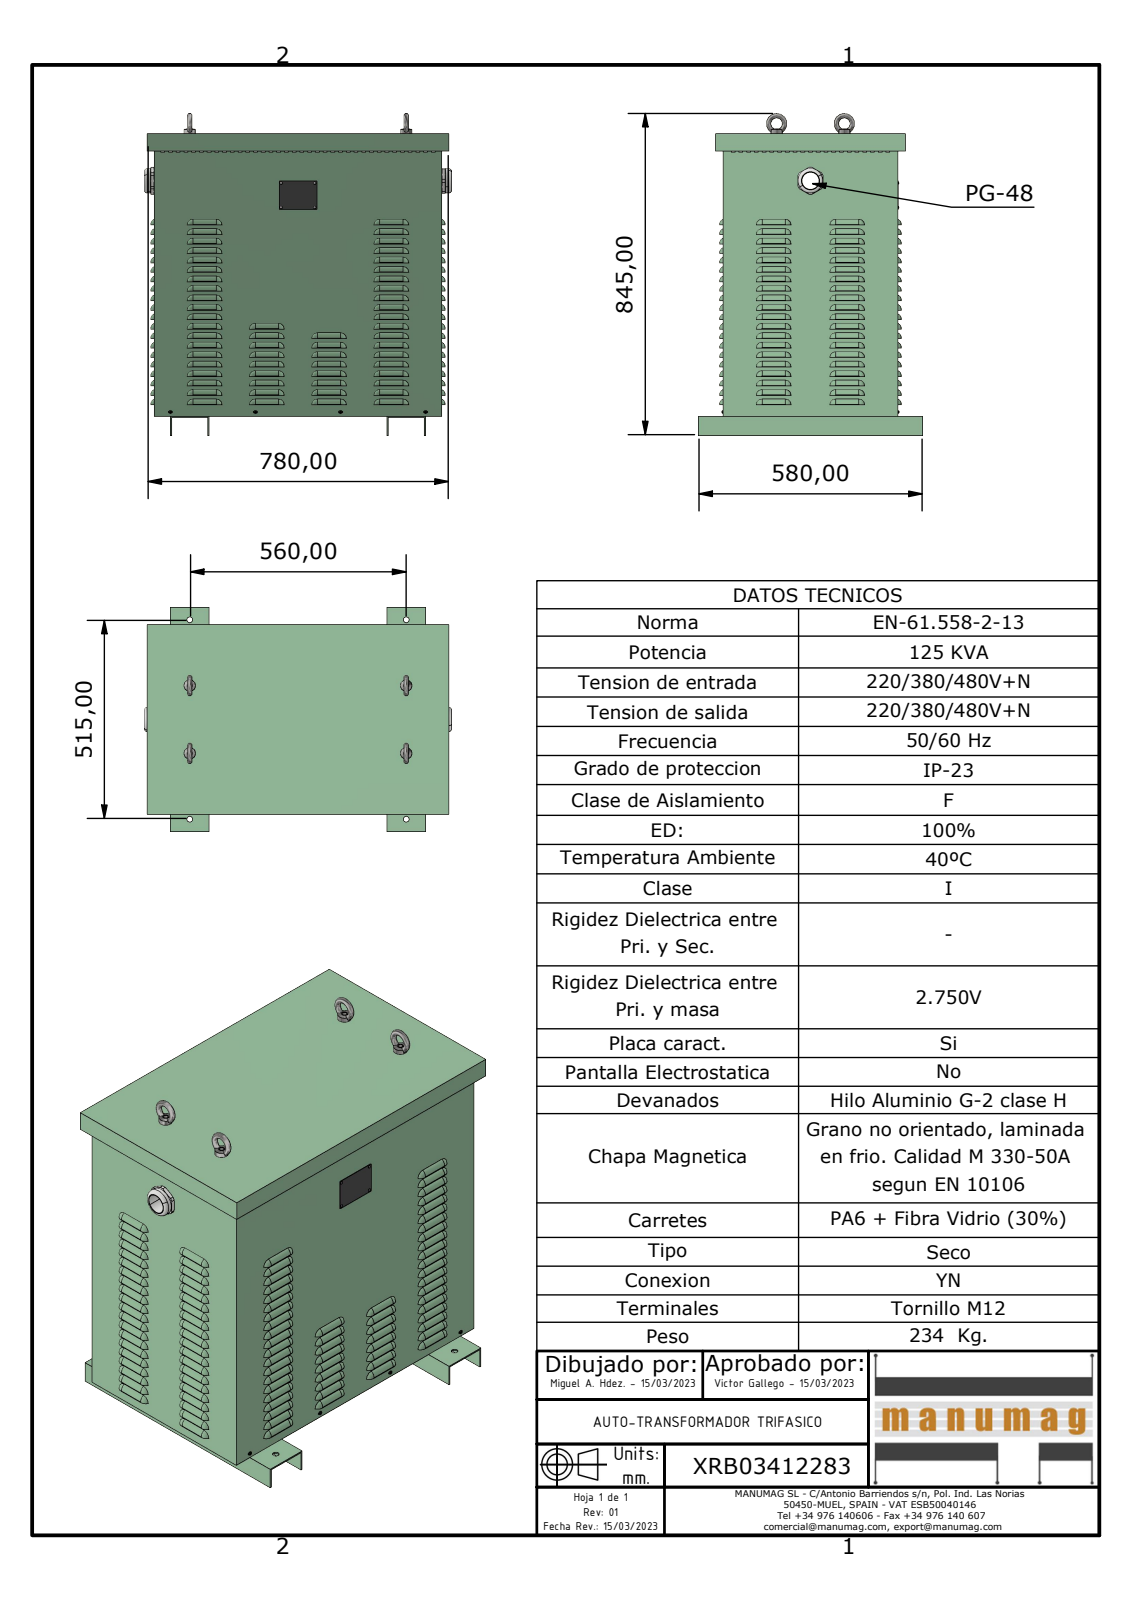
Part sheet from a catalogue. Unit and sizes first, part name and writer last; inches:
Units: inches
Overall size (bounding box): 32.874 × 31.31 × 22.835
Round holes (diameter × count): ⌀0.433 ×780, ⌀0.591 ×8, ⌀0.157 ×4, ⌀0.197 ×4, ⌀0.398 ×4, ⌀1.732 ×1, ⌀2.362 ×1
Round bosses / shafts (diameter × count): ⌀1.181 ×4, ⌀0.157 ×4, ⌀0.143 ×4, ⌀0.126 ×4, ⌀2.48 ×1, ⌀2.335 ×1, ⌀2.329 ×1, ⌀2.269 ×1
Partial cylindrical surfaces — rounded edges, fillets, slot ends (radius × count): R0.551 ×194, R0.276 ×80, R0.591 ×80, R0.098 ×8, R0.079 ×4, R1.378 ×1
Main face-to-face distances: 0.079, 17.717, 28.74, 29.213, 17.638, 17.795, 28.819, 29.134, 28.661, 29.291
Hole centre spacings: 0.819, 6.481, 1.31, 5.893, 7.047, 1.181, 1.86, 5.866
Volume: 407.2 in³ · Surface area: 9 164 in²
Bodies: 24 solids, 4123 faces (1445 planar, 1686 cylindrical, 992 other)
Part name (STEP PRODUCT): XRB03412283; JE125 - JE160NACIONAL CUERPO; JE125 JE160 NACIONAL BASE; JE125 - JE160 NACIONAL PATA (+6 more)
STEP written by: Autodesk Inventor 2023 (AUTOMOTIVE_DESIGN)
